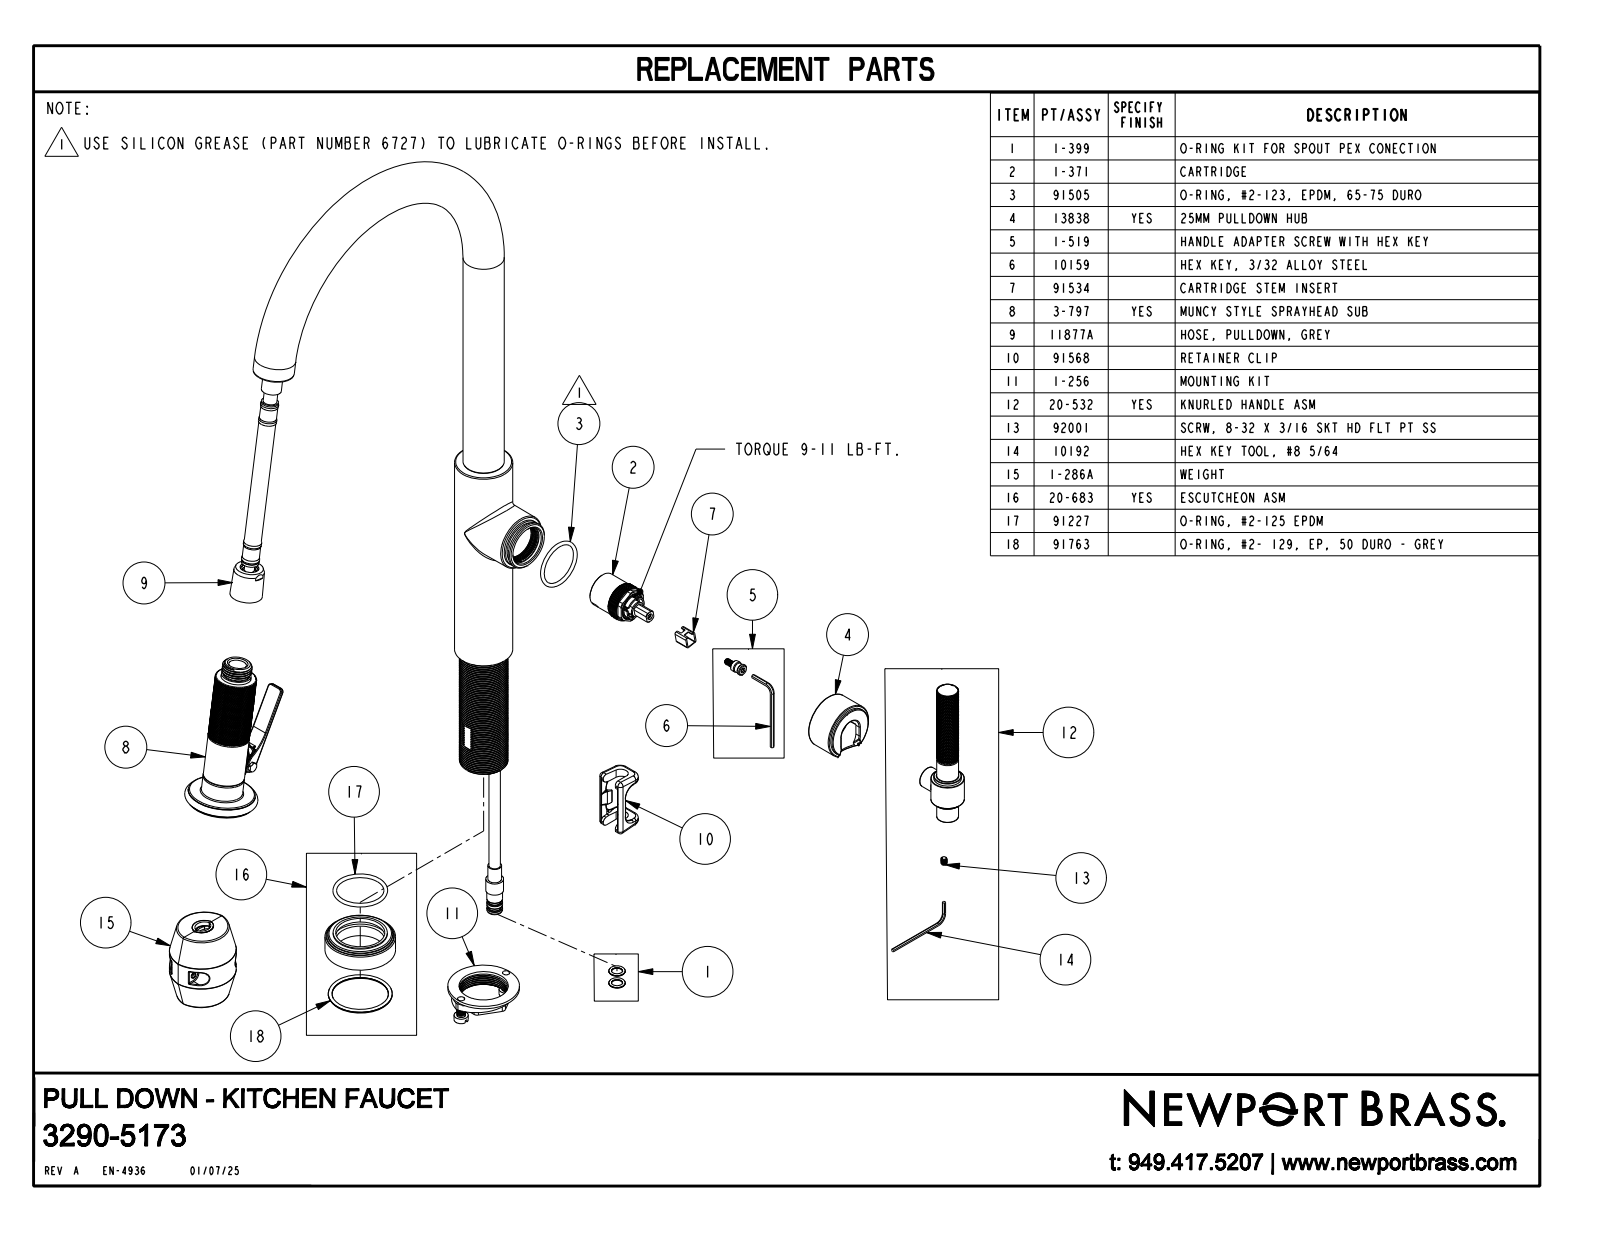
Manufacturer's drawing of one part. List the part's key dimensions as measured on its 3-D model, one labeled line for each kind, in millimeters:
Part name (STEP PRODUCT): 3290-5143_ASM_SW0001
STEP written by: CREO PARAMETRIC BY PTC INC, 2023134 (CONFIG_CONTROL_DESIGN)
Units: millimetres
Bodies: 1 solid, 21816 faces (1300 planar, 4093 cylindrical, 16423 other)
Overall size (bounding box): 466.5 × 272 × 119
Volume: 719 600 mm³ · Surface area: 104 400 mm²
Round holes (diameter × count): ⌀1 ×18, ⌀4.3 ×1, ⌀5.3 ×1, ⌀12 ×1, ⌀14.2 ×1, ⌀26.3 ×1
Round bosses / shafts (diameter × count): ⌀2.6 ×18, ⌀29 ×2, ⌀29 ×2, ⌀49.3 ×1, ⌀47.1 ×1, ⌀45.2 ×1, ⌀40.6 ×1, ⌀39.6 ×1
Partial cylindrical surfaces — rounded edges, fillets, slot ends (radius × count): R0.5 ×26, R0.8 ×23, R1.5 ×15, R0.6 ×7, R1.1 ×4, R2.5 ×3, R1.7 ×2, R5.1 ×2
Main face-to-face distances: 7.8, 174.2, 2.5, 1, 6.8, 15.9, 14, 160.3, 43.8, 59.7
Hole centre spacings: 9.3, 9.3, 16.2, 17.6, 12, 3.3, 6.4, 9.4
